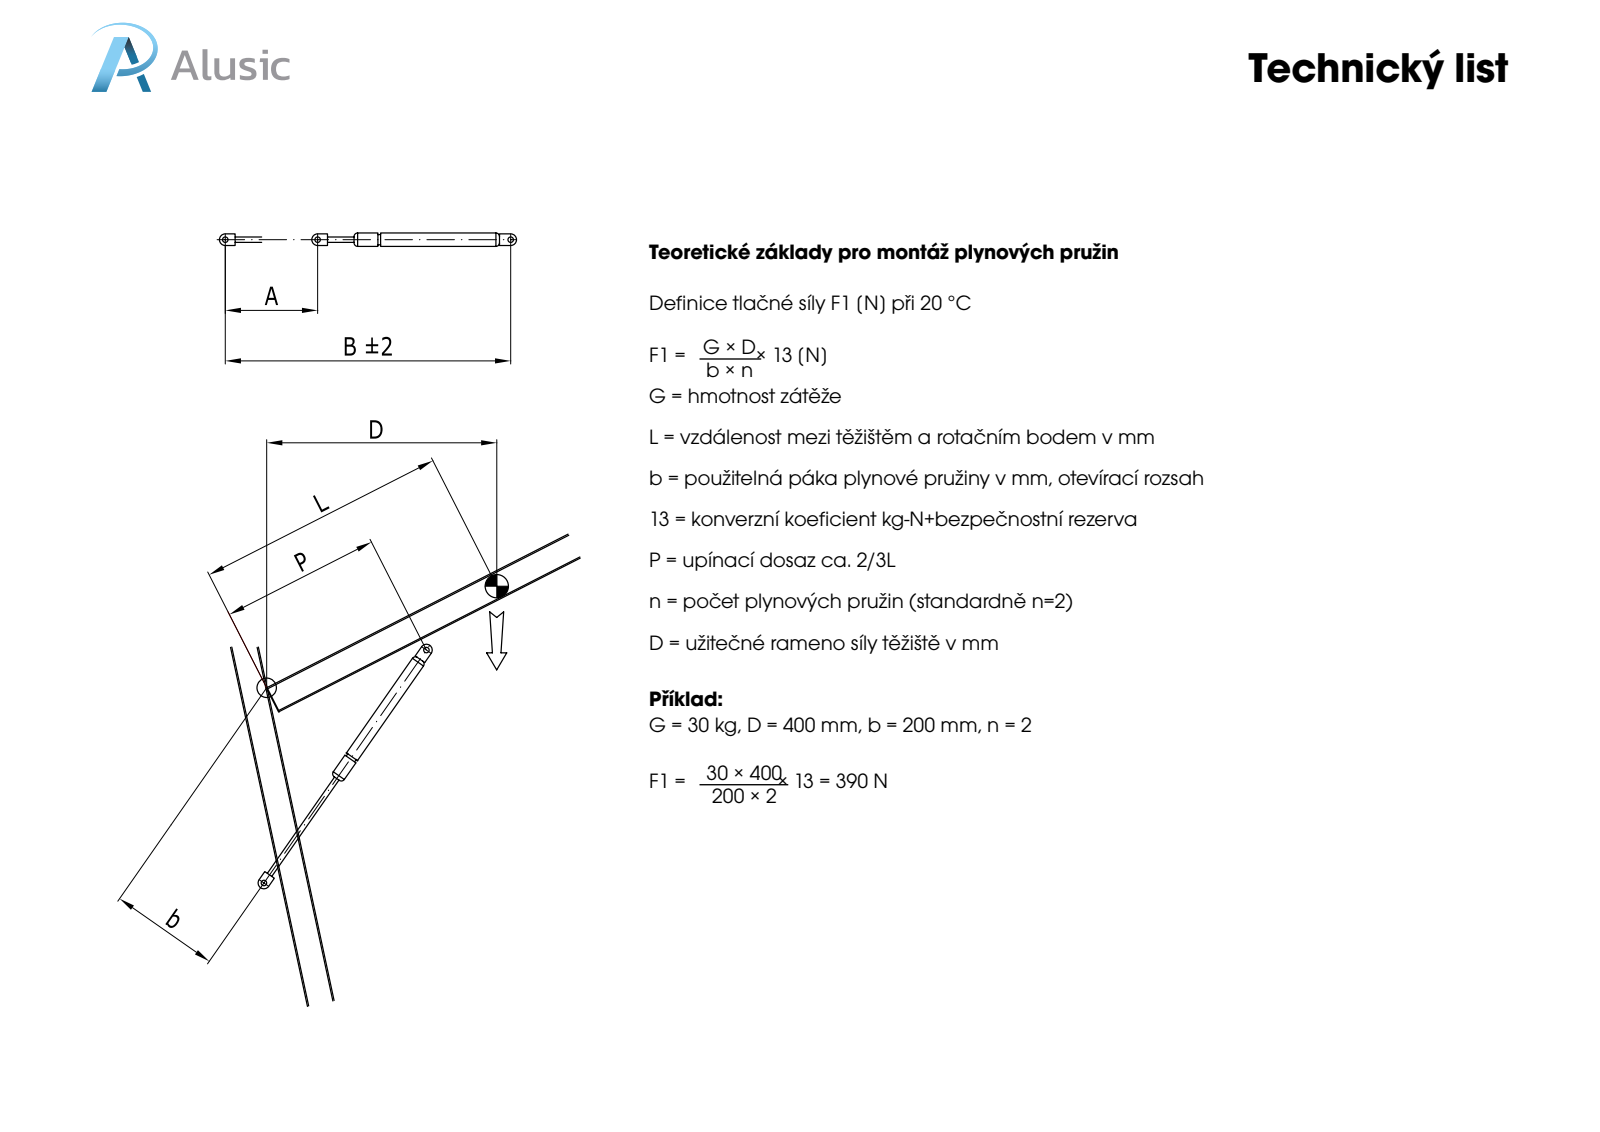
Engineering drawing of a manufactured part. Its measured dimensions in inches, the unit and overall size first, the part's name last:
Units: inches
Overall size (bounding box): 7.008 × 0.591 × 0.591
Round holes (diameter × count): ⌀0.248 ×2
Round bosses / shafts (diameter × count): ⌀0.591 ×1, ⌀0.236 ×1
Partial cylindrical surfaces — rounded edges, fillets, slot ends (radius × count): R0.256 ×2
Main face-to-face distances: 0.118, 0.512, 0.433, 4.882, 5.315, 0.236, 5.118, 5.551
Hole centre spacings: 6.496
Volume: 1.688 in³ · Surface area: 15.55 in²
Bodies: 2 solids, 30 faces (16 planar, 10 cylindrical, 4 other)
Part name (STEP PRODUCT): 084.527.002 - CORPO; 084.527.002 - STELO; 084.527.002
STEP written by: SolidWorks 2011 (CONFIG_CONTROL_DESIGN)
